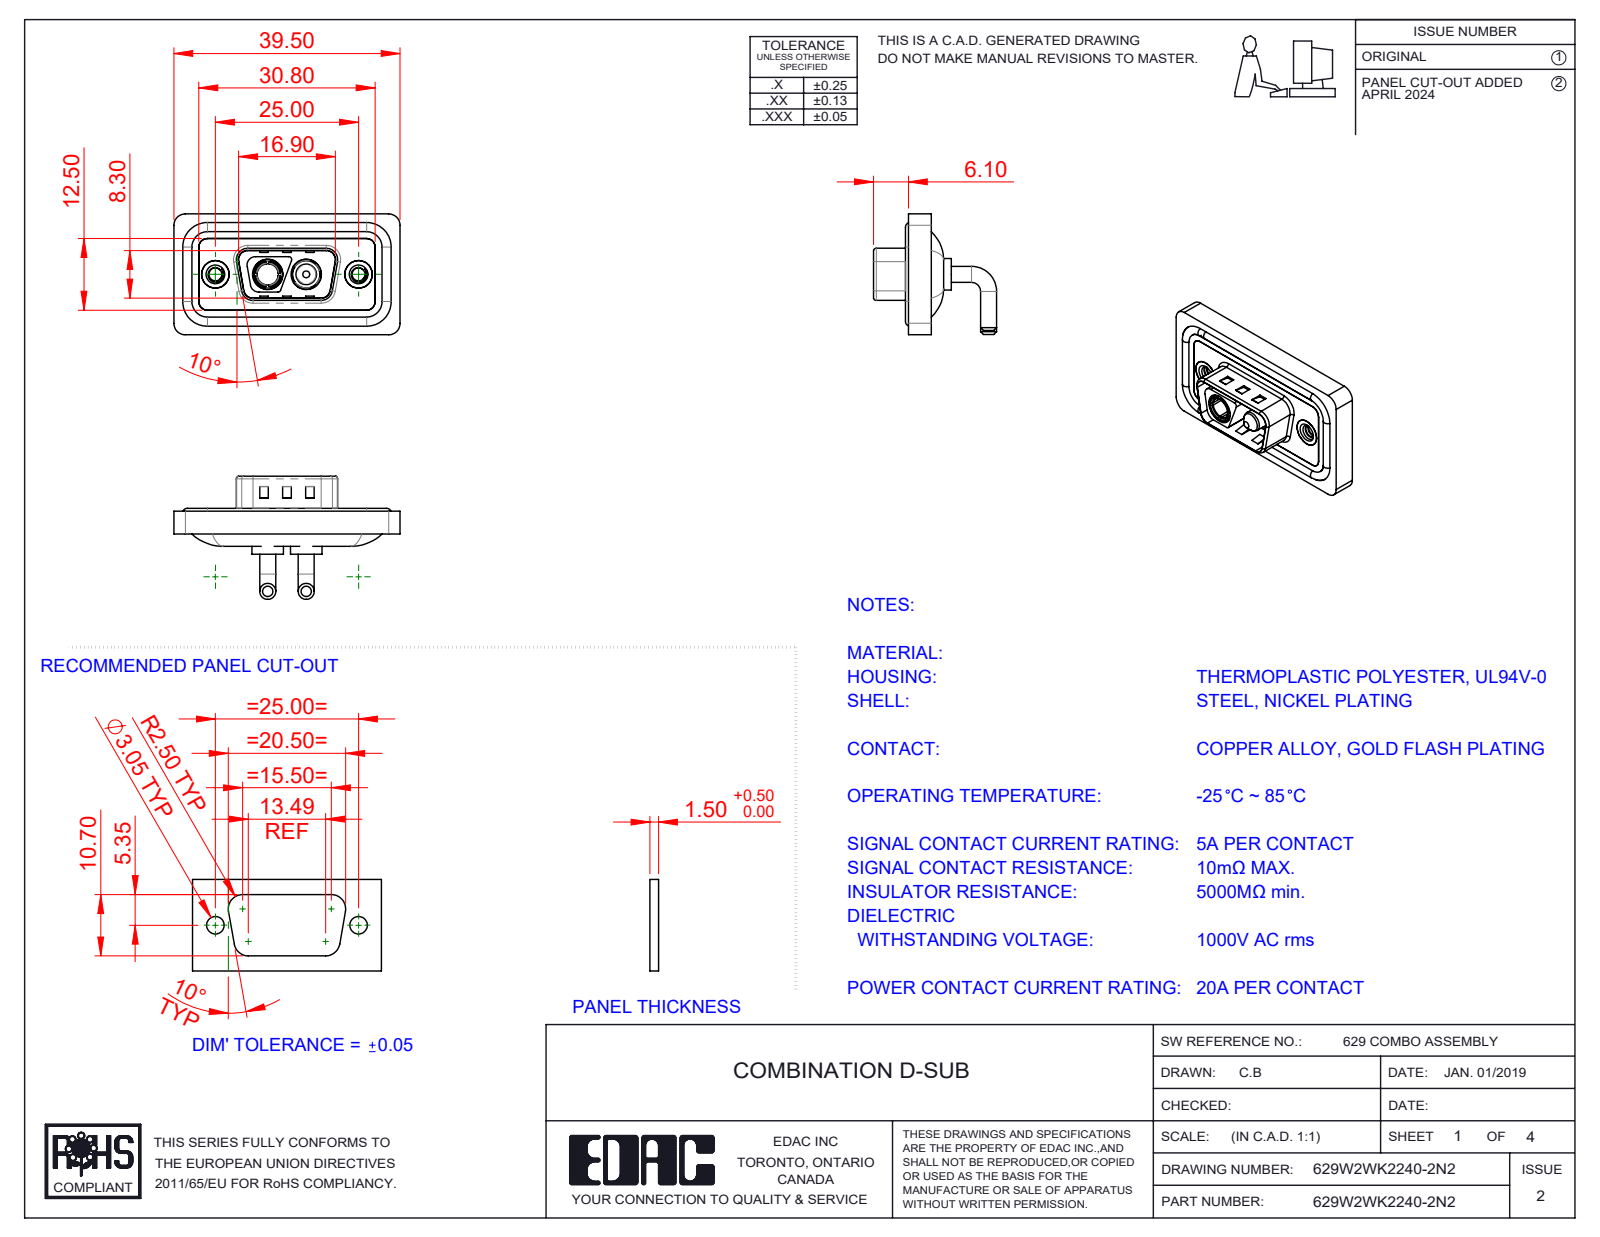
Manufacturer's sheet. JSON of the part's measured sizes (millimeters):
{"part_name": "629Combo Waterproof Housing_09 Contacts; Power Pin_20A RA; 629W2WK2240-2N2; 629Combo Shell Front_09 Contacts (+4 more)", "step_written_by": "SolidWorks 2023 (CONFIG_CONTROL_DESIGN)", "units": "millimeters", "bodies": {"solids": 11, "faces": 542, "planar": 189, "cylindrical": 231, "other": 122}, "overall_size": [39.5, 21.5, 21.1], "volume_mm3": 4693, "surface_area_mm2": 7532, "round_holes": [[2.26, 2], [4, 2], [4.8, 2], [4.85, 2], [5, 2], [5.3, 2], [3.7, 1]], "round_bosses_or_shafts": [[2.8, 4], [1.6, 4], [5.5, 2], [5.2, 2], [4.9, 2], [4.75, 2], [3.75, 2], [4.96, 1]], "partial_cylinders_radius": [[1.5, 20], [2, 18], [0.5, 10], [1.6, 8], [0.25, 4], [0.6, 4], [0.65, 4], [0.9, 4]], "face_to_face_distances": [0.4, 2.9, 1.1, 0.8, 2.1, 2.5, 3.1, 1.6, 4.5, 1.5], "hole_center_spacings": [9.14, 15.86, 6.72, 25]}
